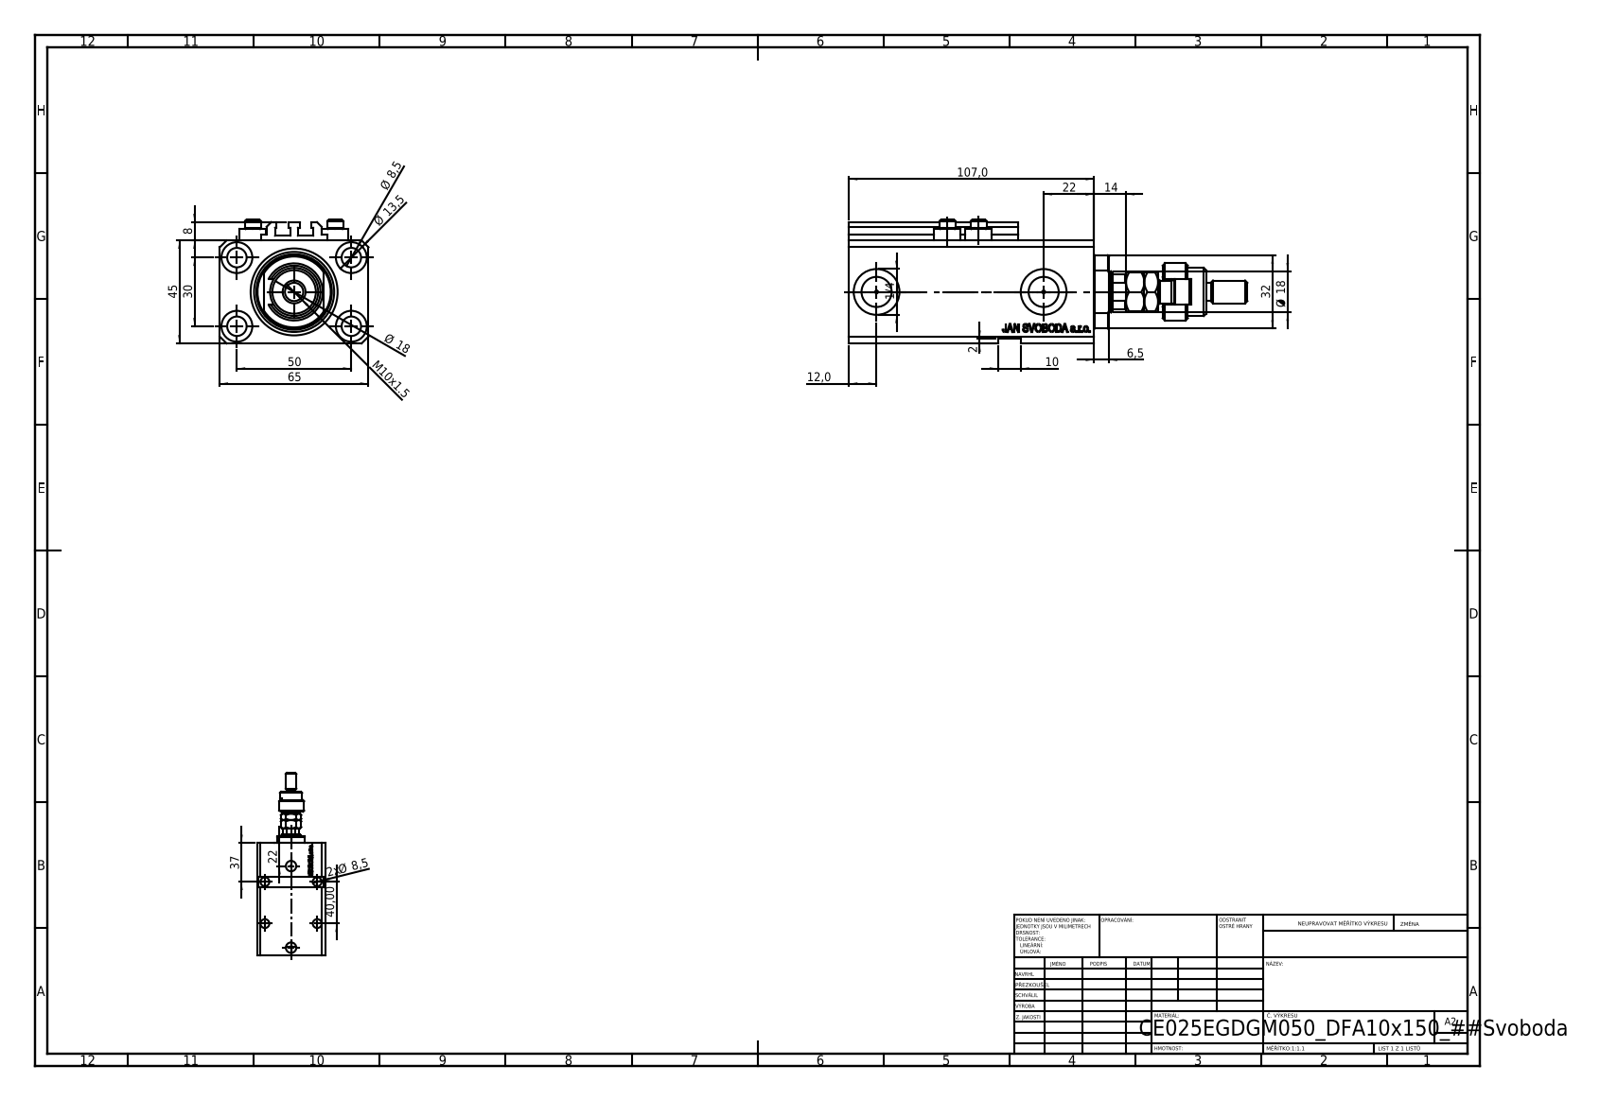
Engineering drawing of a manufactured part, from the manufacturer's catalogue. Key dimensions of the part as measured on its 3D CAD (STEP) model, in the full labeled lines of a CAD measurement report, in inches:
Part name (STEP PRODUCT): V250CE_C_VCP; FEMALE_PART_FOR_DFA; ALLEN BOLT V250CE; MFA (+2 more)
STEP written by: SolidWorks 2019 (CONFIG_CONTROL_DESIGN)
Units: inches
Bodies: 10 solids, 1188 faces (543 planar, 171 cylindrical, 474 other)
Overall size (bounding box): 6.85 × 2.559 × 2.126
Volume: 17.18 in³ · Surface area: 129.4 in²
Round holes (diameter × count): ⌀0.335 ×9, ⌀0.049 ×4, ⌀0.157 ×4, ⌀0.531 ×4, ⌀0.394 ×2, ⌀0.518 ×2, ⌀0.787 ×2, ⌀0.709 ×1, ⌀1.496 ×1
Round bosses / shafts (diameter × count): ⌀0.457 ×4, ⌀0.276 ×4, ⌀0.984 ×1, ⌀0.827 ×1, ⌀0.63 ×1, ⌀0.394 ×1, ⌀0.315 ×1
Partial cylindrical surfaces — rounded edges, fillets, slot ends (radius × count): R0.008 ×10, R0.217 ×1, R0.335 ×1, R0.344 ×1, R0.63 ×1
Main face-to-face distances: 1.772, 2.559, 0.551, 0.079, 3.661, 1.85, 4.213, 0.098, 0.118, 0.394
Hole centre spacings: 1.148, 1.969, 0.535, 0.581, 0.595, 1.083, 1.098, 1.181
